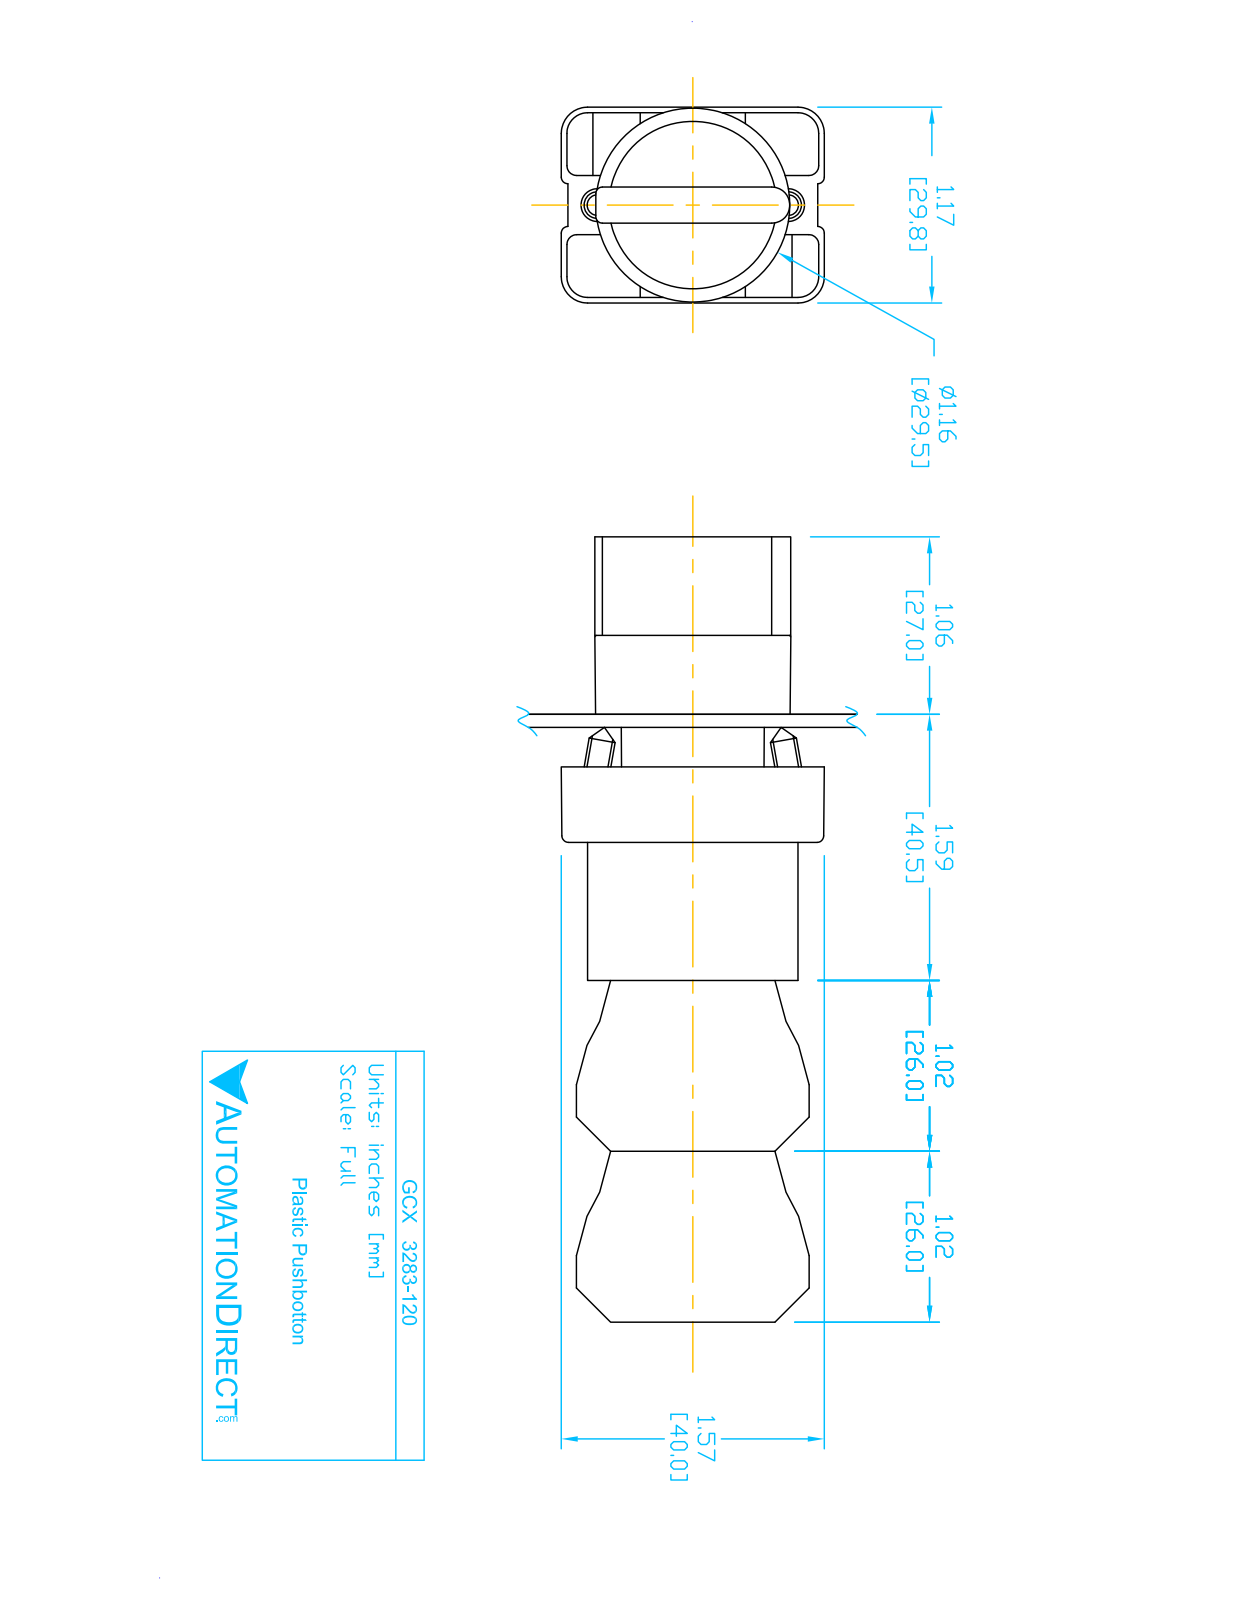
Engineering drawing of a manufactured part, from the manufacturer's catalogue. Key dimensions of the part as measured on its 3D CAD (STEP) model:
Part name (STEP PRODUCT): ecx1030; ECX3029-2; GCX3283-120; ecx1040 (+2 more)
STEP written by: SolidWorks 2016 (AUTOMOTIVE_DESIGN)
Units: inches
Bodies: 11 solids, 724 faces (488 planar, 193 cylindrical, 43 other)
Overall size (bounding box): 4.677 × 1.581 × 1.177
Volume: 4.751 in³ · Surface area: 59.22 in²
Round holes (diameter × count): ⌀0.079 ×4, ⌀0.087 ×2, ⌀0.124 ×2, ⌀0.13 ×2, ⌀0.197 ×1, ⌀0.469 ×1, ⌀0.878 ×1, ⌀0.888 ×1, ⌀1.024 ×1
Round bosses / shafts (diameter × count): ⌀0.157 ×4, ⌀1.175 ×1, ⌀1.004 ×1, ⌀0.945 ×1, ⌀0.856 ×1, ⌀0.78 ×1, ⌀0.504 ×1
Partial cylindrical surfaces — rounded edges, fillets, slot ends (radius × count): R0.059 ×24, R0.041 ×12, R0.124 ×12, R0.157 ×12, R0.039 ×9, R0.02 ×2, R0.063 ×2, R0.079 ×2
Main face-to-face distances: 0.579, 0.593, 1.024, 1.171, 0.014, 0.827, 1.85, 3.043, 2.02, 1.193
Hole centre spacings: 0.236, 1.003, 0.974, 0.472, 0.539, 0.544, 1.083, 0.484
